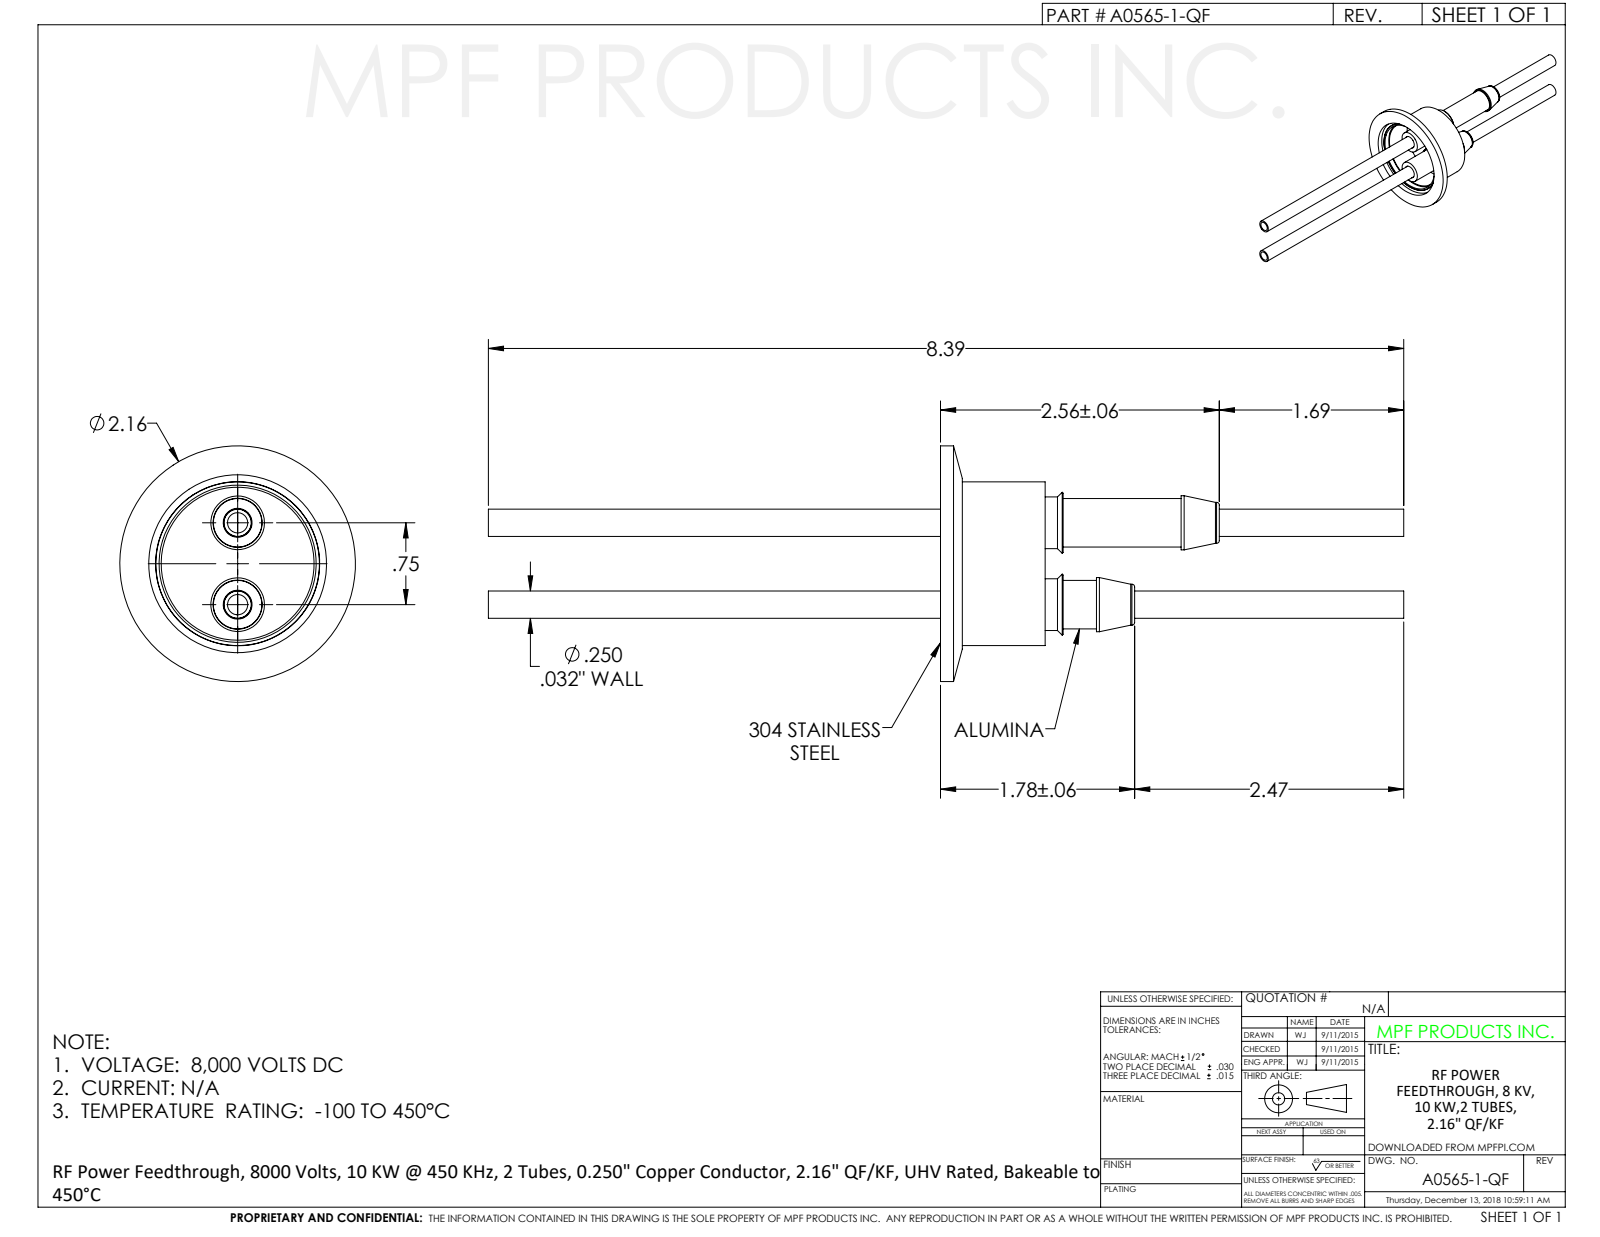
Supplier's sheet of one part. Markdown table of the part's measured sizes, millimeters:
| quantity | value |
| --- | --- |
| part name | A0565-1-QF |
| STEP written by | SolidWorks 2012 (CONFIG_CONTROL_DESIGN) |
| units | millimeters |
| bodies | 1 solid, 136 faces (24 planar, 58 cylindrical, 54 other) |
| overall size | 213.1 × 54.9 × 54.9 |
| volume | 22 840 mm³ |
| surface area | 31 390 mm² |
| round holes (diameter × count) | 6.7 × 2, 12.5 × 2, 14 × 2, 4.6 × 1, 4.7 × 1, 35.6 × 1, 36.7 × 1, 36.8 × 1, 41.2 × 1 |
| round bosses / shafts (diameter × count) | 14.5 × 2, 12.6 × 2, 12 × 2, 11.3 × 2, 6.4 × 2, 54.9 × 1, 38.1 × 1 |
| main face-to-face distances | 3.2, 21.5, 18.4, 2.5, 15.9, 19.1, 5.1, 2.6, 13.3, 16.5 |
| hole center spacings | 9.5, 9.5, 19.1 |
